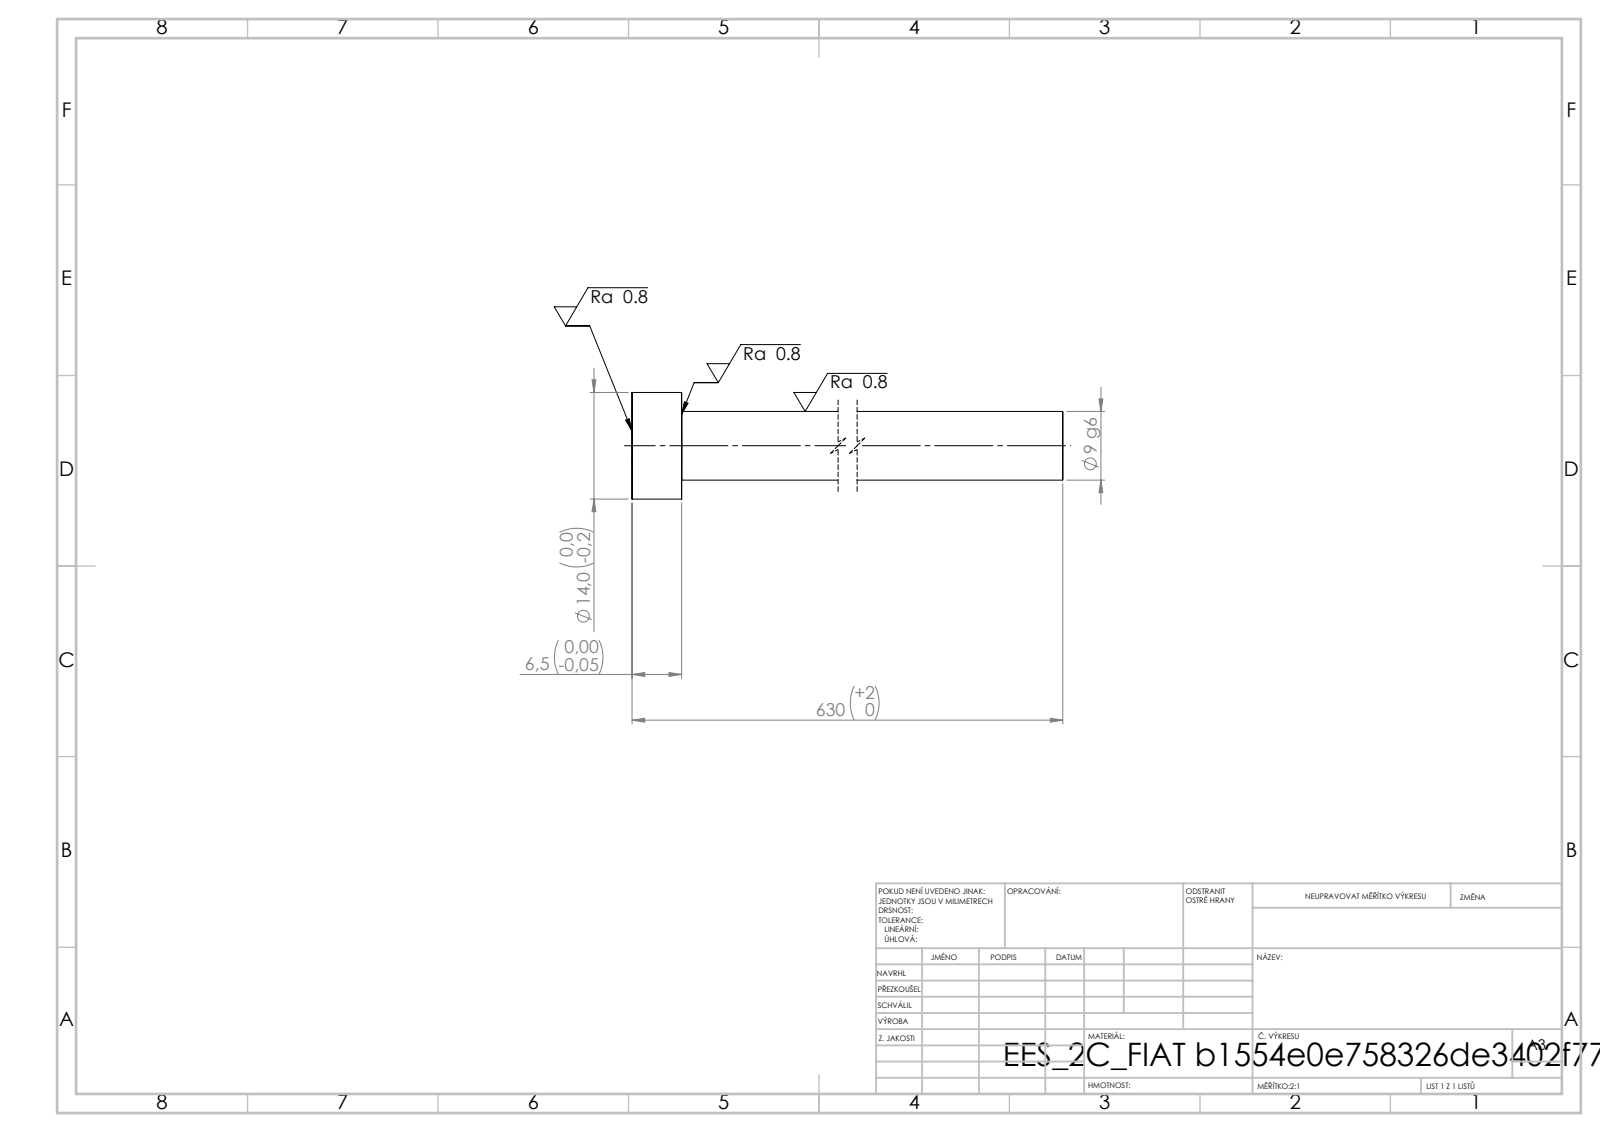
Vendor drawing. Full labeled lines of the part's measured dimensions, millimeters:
STEP written by: SolidWorks 2019 (CONFIG_CONTROL_DESIGN)
Units: millimetres
Bodies: 1 solid, 7 faces (3 planar, 4 cylindrical, 0 other)
Overall size (bounding box): 630 × 14 × 14
Volume: 40 666 mm³ · Surface area: 18 223 mm²
Round bosses / shafts (diameter × count): ⌀14 ×1, ⌀9 ×1
Main face-to-face distances: 6.5, 630, 623.5
